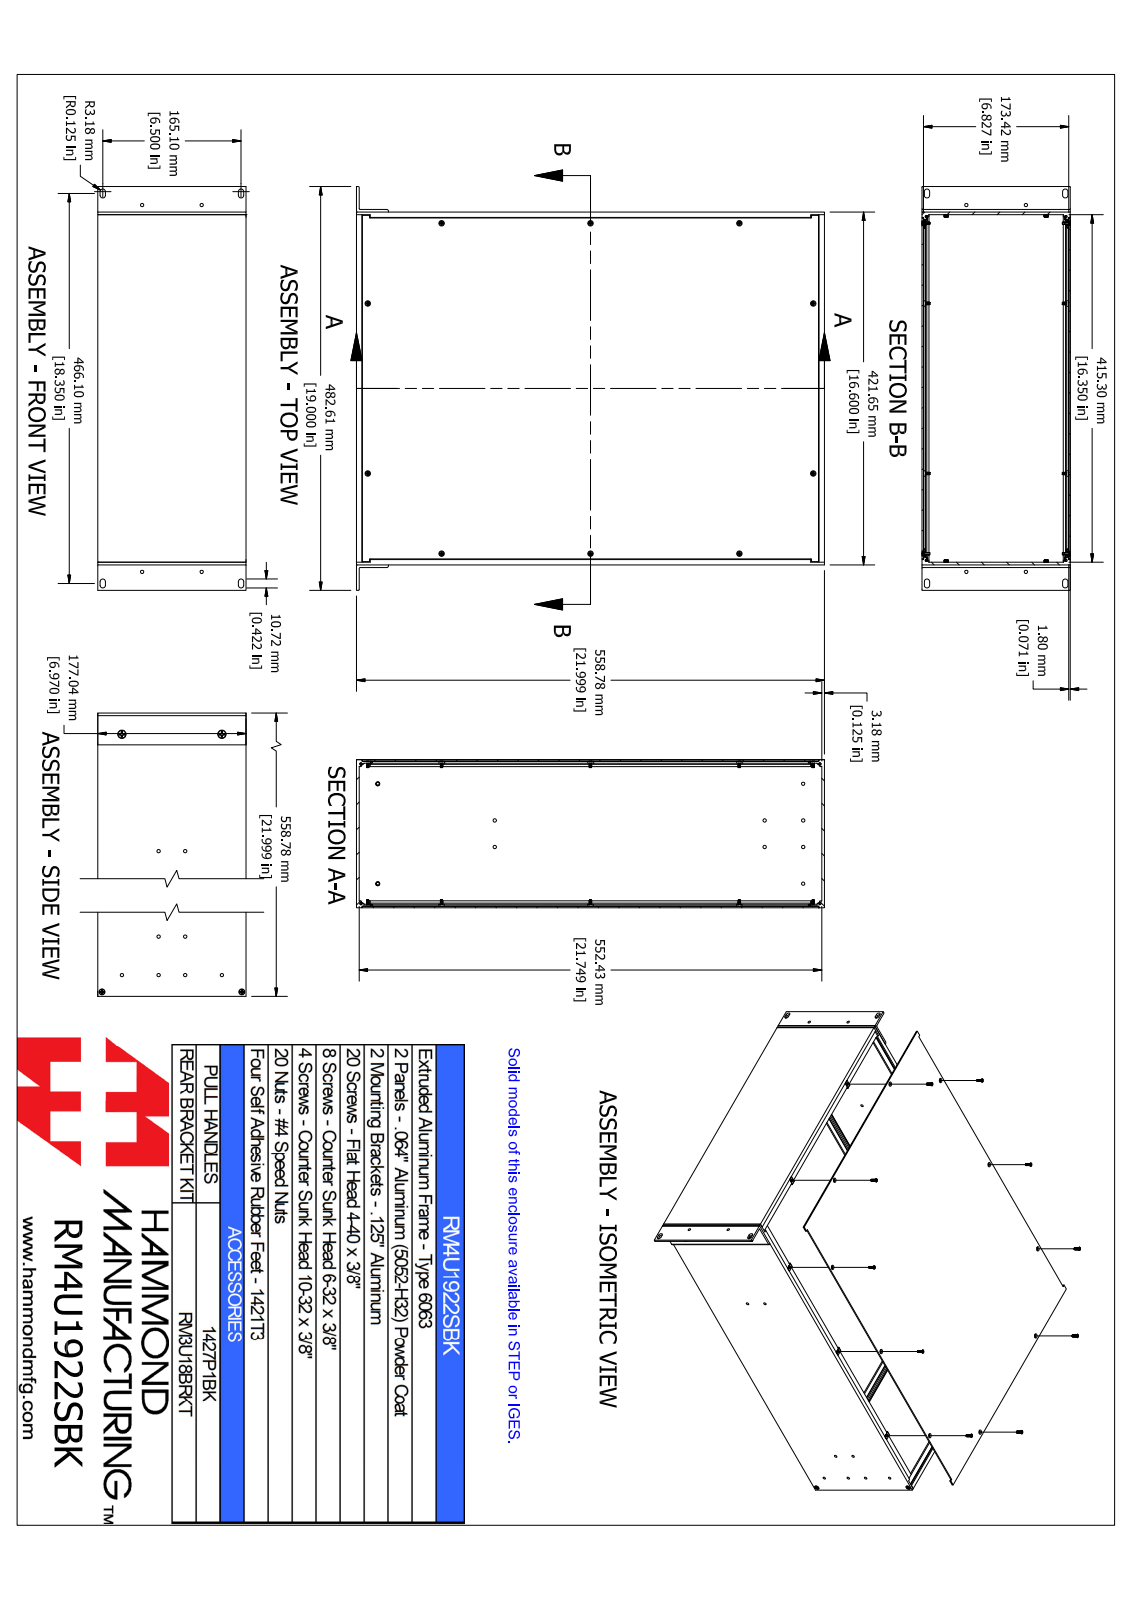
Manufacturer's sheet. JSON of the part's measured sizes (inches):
{"part_name": "RM4U1922SBK", "step_written_by": "SolidWorks 2021 (AUTOMOTIVE_DESIGN)", "units": "inches", "bodies": {"solids": 60, "faces": 2284, "planar": 952, "cylindrical": 544, "other": 788}, "overall_size": [21.999, 19, 6.971], "volume_in3": 129.9, "surface_area_in2": 2759, "round_holes": [[0.157, 10], [0.16, 10], [0.159, 6], [0.165, 6], [0.138, 4], [0.156, 4], [0.157, 4], [0.169, 4], [0.197, 2]], "round_bosses_or_shafts": [[0.2, 10], [0.112, 10], [0.238, 4], [0.138, 4], [0.36, 2], [0.19, 2]], "partial_cylinders_radius": [[0.01, 80], [0.024, 80], [0.009, 40], [0.014, 40], [0.015, 16], [0.038, 16], [0.039, 14], [0.035, 9]], "face_to_face_distances": [0.071, 6.899, 6.97, 6.898, 0.071, 6.828, 16.476, 0.125, 0.125, 21.874], "hole_center_spacings": [7, 5.127, 17.049, 8, 11.131, 12.274, 14, 15.756]}
